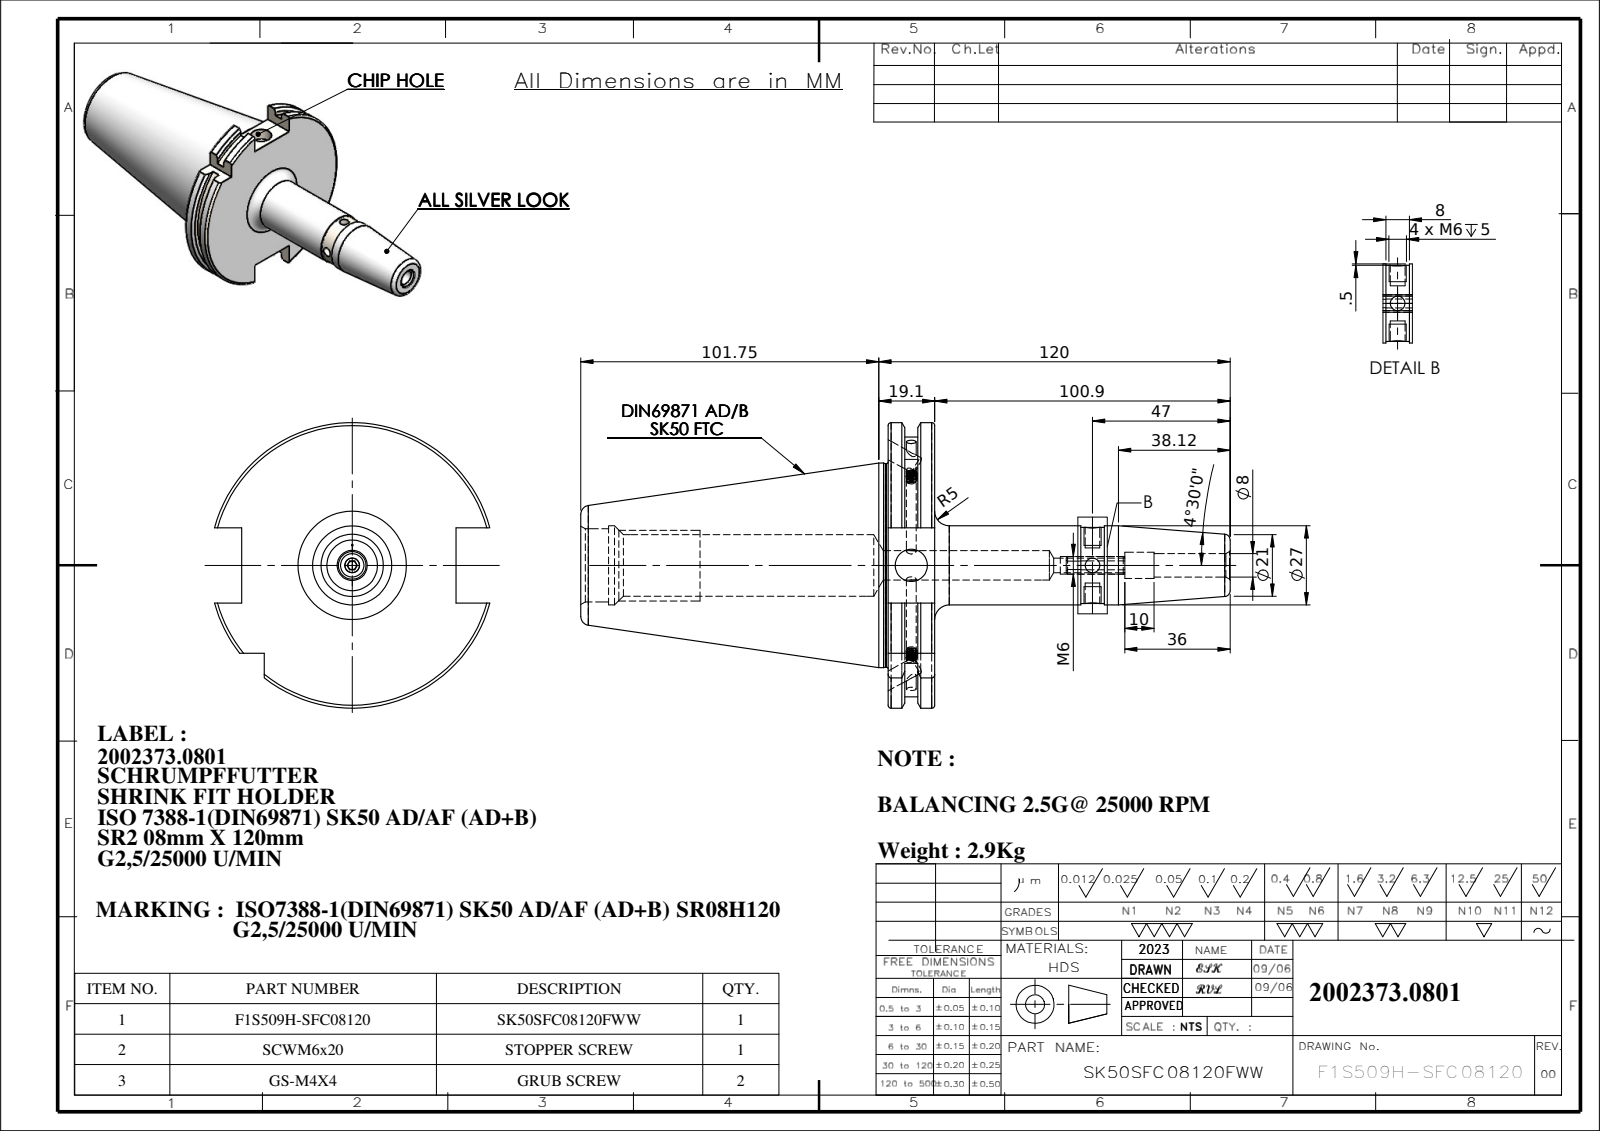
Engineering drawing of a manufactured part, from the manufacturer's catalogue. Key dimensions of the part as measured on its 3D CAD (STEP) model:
Part name (STEP PRODUCT): SK50SFC08120FWW; 91506-SR208120; GS-M4X4_DIN 913 - M4 x 4-N; SCWM6
STEP written by: SolidWorks 2018 (CONFIG_CONTROL_DESIGN)
Units: millimetres
Bodies: 4 solids, 247 faces (58 planar, 83 cylindrical, 106 other)
Overall size (bounding box): 221.75 × 97.5 × 94.05
Volume: 370 492 mm³ · Surface area: 56 471 mm²
Round holes (diameter × count): ⌀5 ×3, ⌀6 ×2, ⌀2.9 ×1, ⌀3.3 ×1, ⌀7.99 ×1, ⌀8.99 ×1, ⌀10 ×1, ⌀11 ×1, ⌀21 ×1, ⌀25 ×1
Round bosses / shafts (diameter × count): ⌀4 ×2, ⌀69.85 ×1, ⌀69.45 ×1, ⌀27 ×1, ⌀26 ×1, ⌀6 ×1
Partial cylindrical surfaces — rounded edges, fillets, slot ends (radius × count): R44.9 ×1, R48.75 ×1
Main face-to-face distances: 15.9, 5.66, 10.24, 10.14, 4.48, 5.76, 104.95, 110.61, 115.09, 120.85
Hole centre spacings: 61.9
